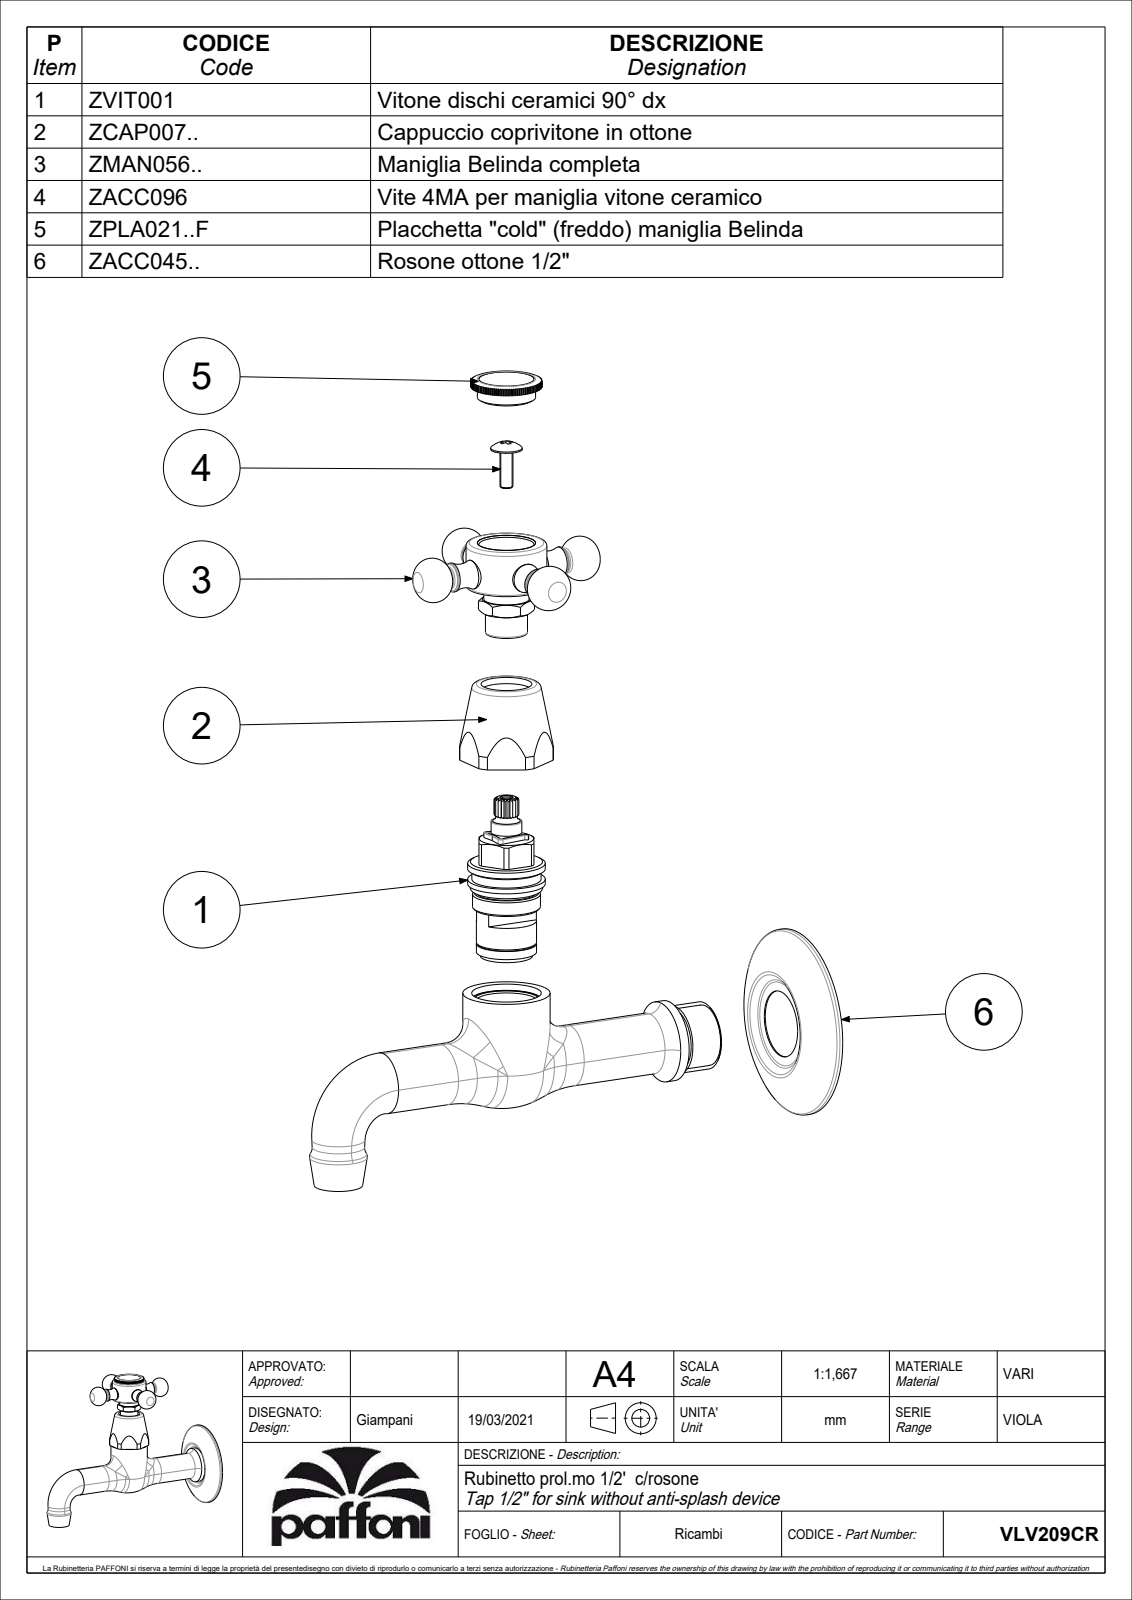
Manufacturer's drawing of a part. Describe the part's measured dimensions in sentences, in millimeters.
The part is named "VLV209CR". Its 3-D file was written by "CREO PARAMETRIC BY PTC INC, 2020044 (CONFIG_CONTROL_DESIGN)". It is 1 solid with 522 faces: 238 planar, 146 cylindrical and 138 other. Overall it measures 139.92 by 105.4 by 64.07 millimeters. Its volume is 95 744 cubic millimeters and its surface area 23 222 square millimeters. Round bosses or shafts: 2 of diameter 25, 2 of diameter 9, 2 of diameter 7, 1 of diameter 58, 1 of diameter 27, 1 of diameter 21, 1 of diameter 14, 1 of diameter 13. Partial cylindrical surfaces (rounded edges, fillets, slot ends): 1 of radius 11, 1 of radius 14.5. The main face-to-face distances are 7.7, 26.5, 5.75, 20.75, 88.7, 77.5, 11.2, 57.75, 84.25, 50.05.
